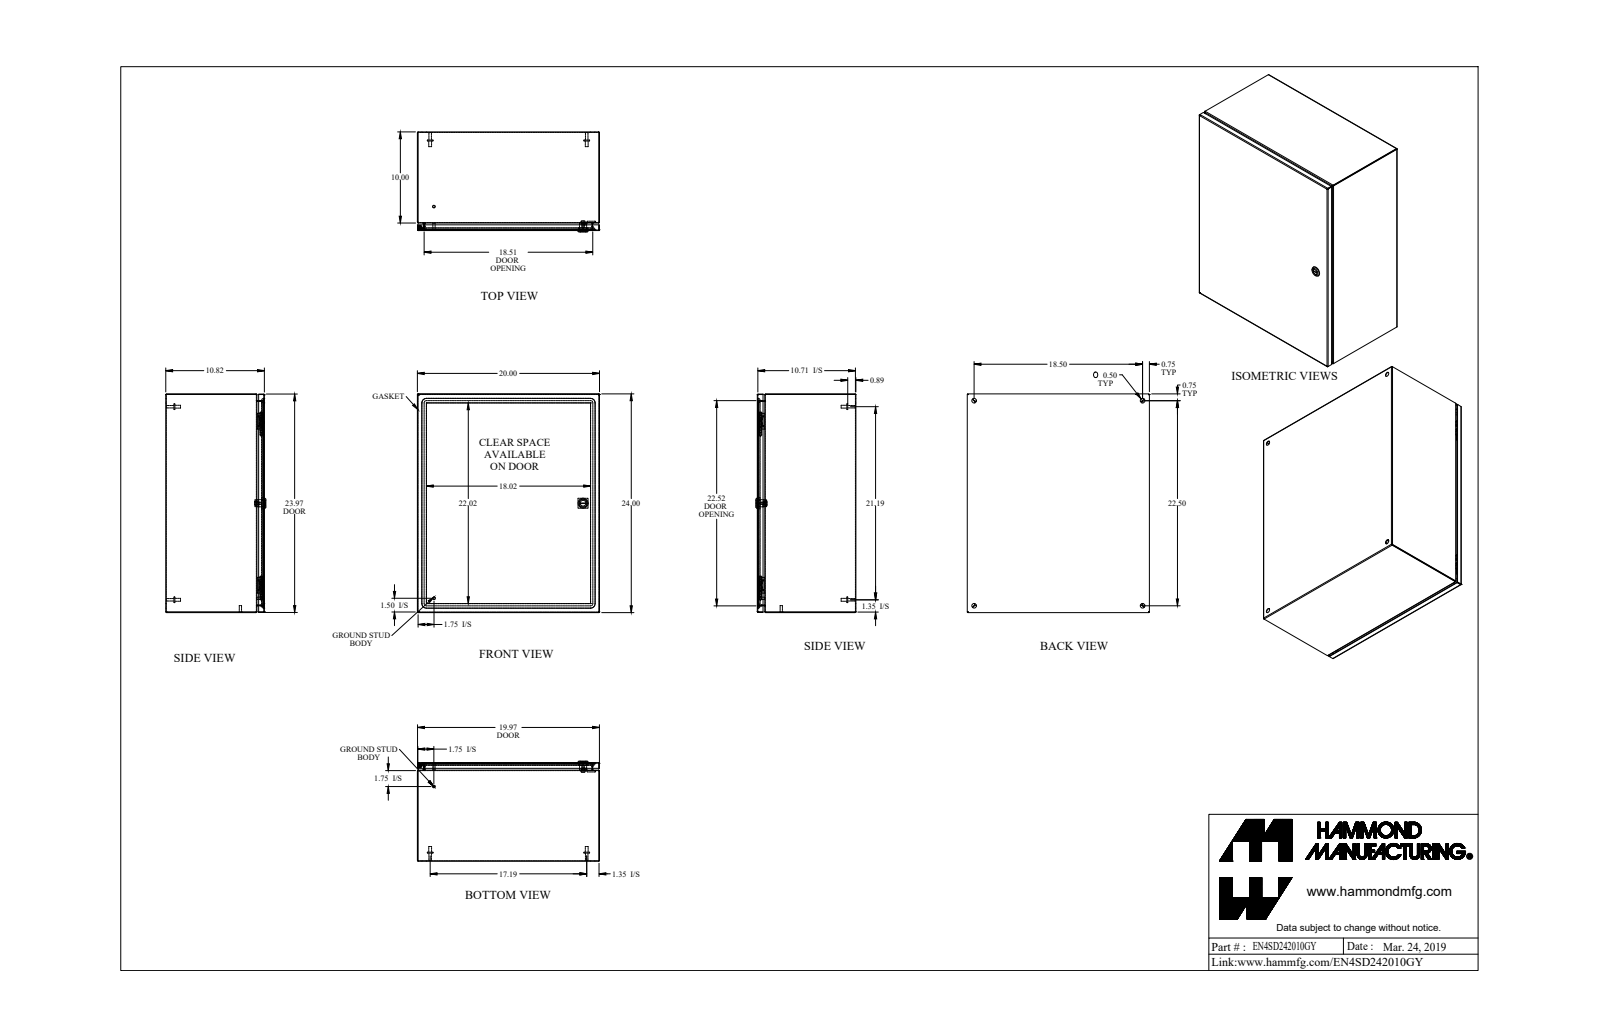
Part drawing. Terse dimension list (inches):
name: EN4SD242010GY_Default
written by: SolidWorks 2019 (CONFIG_CONTROL_DESIGN)
unit: in
bodies: 21 solids, 634 faces (285 planar, 213 cylindrical, 136 other)
size: 24 × 20 × 10.982
volume: 123.2 in³; area: 4 216 in²
holes: 4× ⌀0.5, 1× ⌀0.172, 1× ⌀0.232, 1× ⌀0.24, 1× ⌀0.242, 1× ⌀0.625, 1× ⌀0.785
bosses: 4× ⌀0.625, 4× ⌀0.313, 4× ⌀0.27, 2× ⌀0.281, 2× ⌀0.25, 1× ⌀1.1, 1× ⌀0.525, 1× ⌀0.455
rounds: 21× R0.029, 21× R0.086, 16× R0.25, 8× R19, 4× R0.006, 4× R0.062, 4× R0.499, 2× R0.125
face distances: 0.057, 10.765, 10.708, 10.822, 19.943, 23.943, 19.886, 20, 23.886, 24
hole spacings: 18.5, 22.5, 29.129, 11.299, 11.3, 20.754, 20.755
